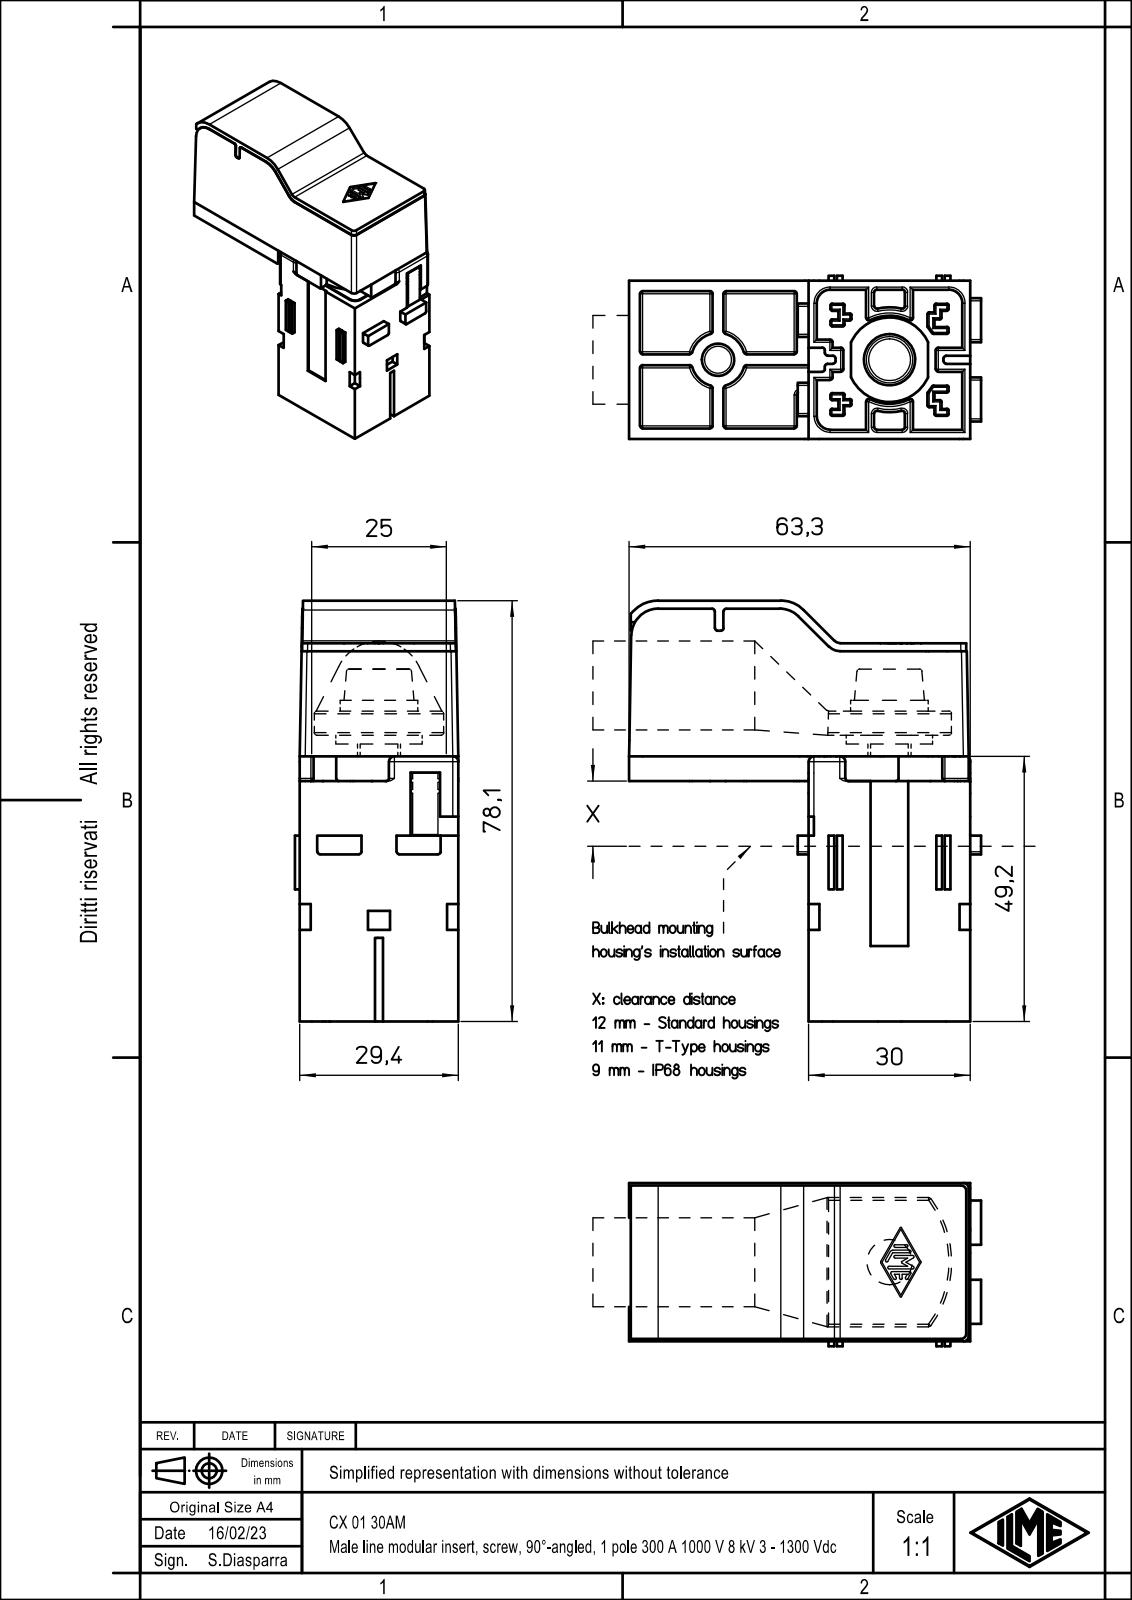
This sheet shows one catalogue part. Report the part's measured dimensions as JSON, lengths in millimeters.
{"part_name": "CX 01 30AM; Insulated cover plate", "step_written_by": "Creo Elements/Direct Modeling 20.1B 02-Apr-2019 (C) Parametric Technology GmbH (AUTOMOTIVE_DESIGN)", "units": "millimeters", "bodies": {"solids": 2, "faces": 996, "planar": 432, "cylindrical": 359, "other": 205}, "overall_size": [78.1, 65.3, 30.3], "volume_mm3": 50685, "surface_area_mm2": 37450, "round_holes": [[6, 1], [17.6, 1]], "round_bosses_or_shafts": [[20.8, 1], [16, 1], [14.4, 1], [9.5, 1], [8, 1]], "partial_cylinders_radius": [[0.5, 112], [0.3, 67], [1, 24], [0.25, 15], [0.35, 8], [0.8, 6], [1.39, 6], [5, 5]], "face_to_face_distances": [2, 27.16, 27.4, 1.85, 1.5, 30, 2.15, 27.25, 25.25, 28], "hole_center_spacings": [31.8]}
